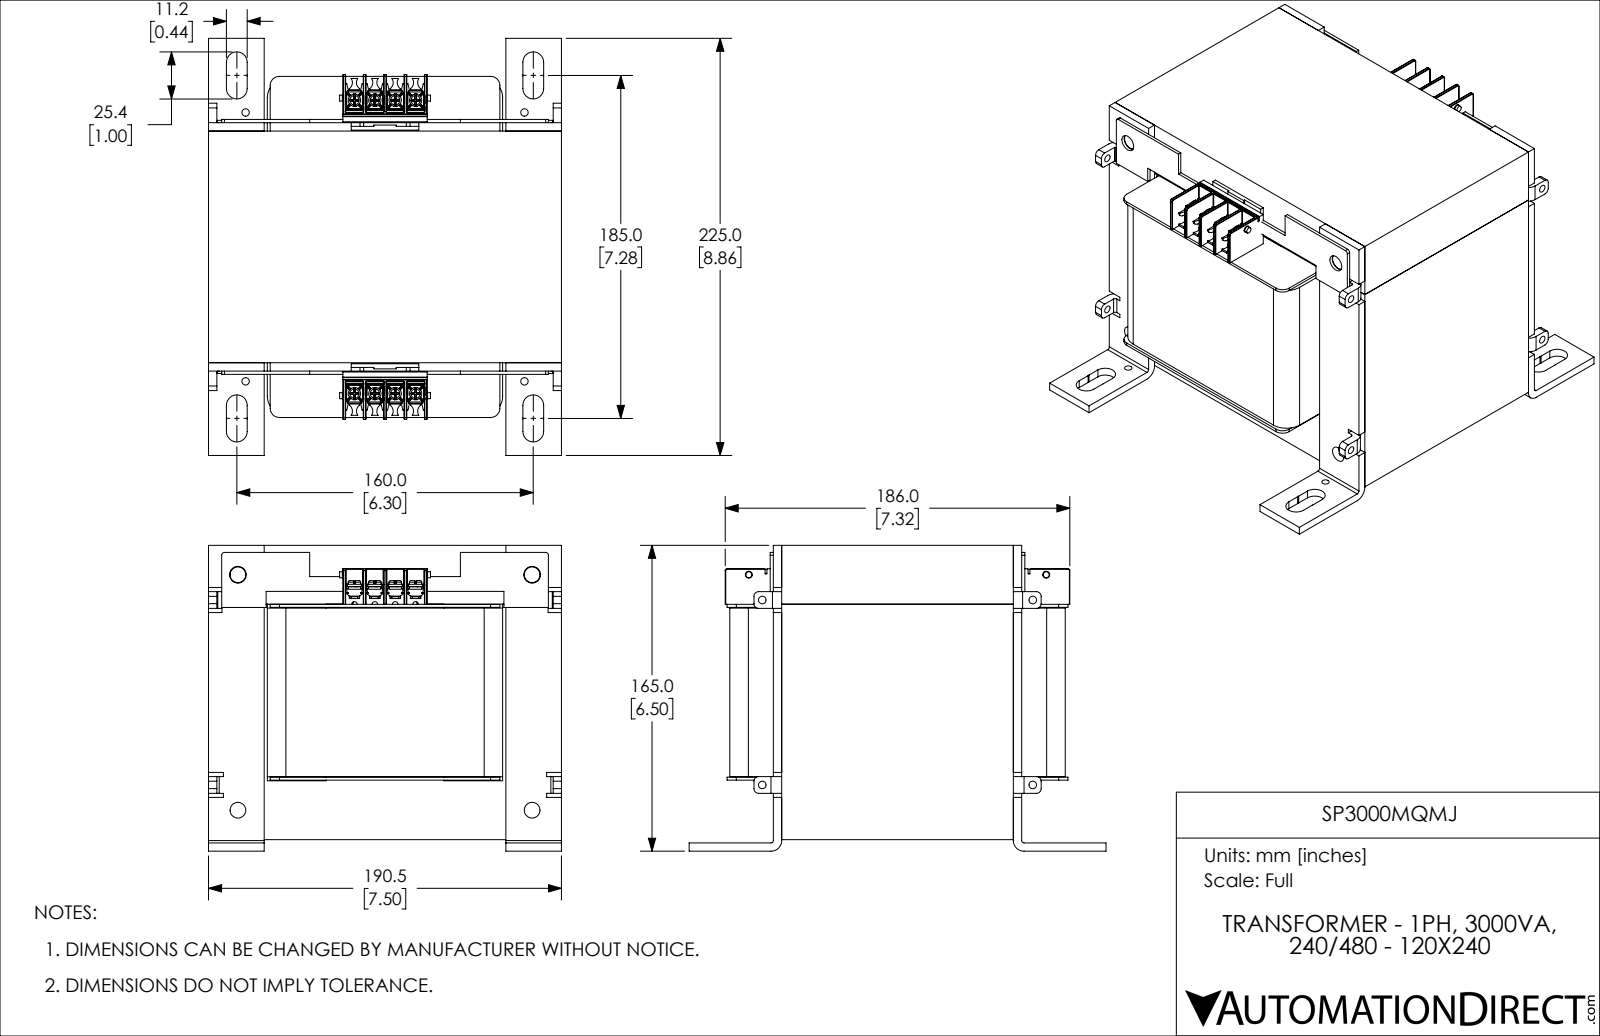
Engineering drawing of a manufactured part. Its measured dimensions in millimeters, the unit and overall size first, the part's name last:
Units: millimetres
Overall size (bounding box): 225 × 190.5 × 165
Round holes (diameter × count): ⌀2.66 ×8, ⌀3.51 ×8, ⌀4 ×4, ⌀4.1 ×4, ⌀8.5 ×4, ⌀9 ×2
Round bosses / shafts (diameter × count): ⌀6.65 ×8, ⌀4.27 ×8, ⌀2.79 ×8, ⌀3.25 ×2
Partial cylindrical surfaces — rounded edges, fillets, slot ends (radius × count): R0.13 ×52, R0.25 ×52, R0.3 ×40, R0.74 ×32, R4 ×16, R0.89 ×12, R2.5 ×8, R5 ×8
Main face-to-face distances: 31.75, 127, 158.75, 93.2, 1.59, 63.5, 125, 95.25, 4.5, 5
Hole centre spacings: 11, 158.58, 22, 59.12, 70.06, 81.02, 91.99, 158.2
Volume: 4 399 000 mm³ · Surface area: 549 158 mm²
Bodies: 37 solids, 3010 faces (1826 planar, 896 cylindrical, 288 other)
Part name (STEP PRODUCT): SP3000MQMJ
STEP written by: SolidWorks 2018 (AUTOMOTIVE_DESIGN)
